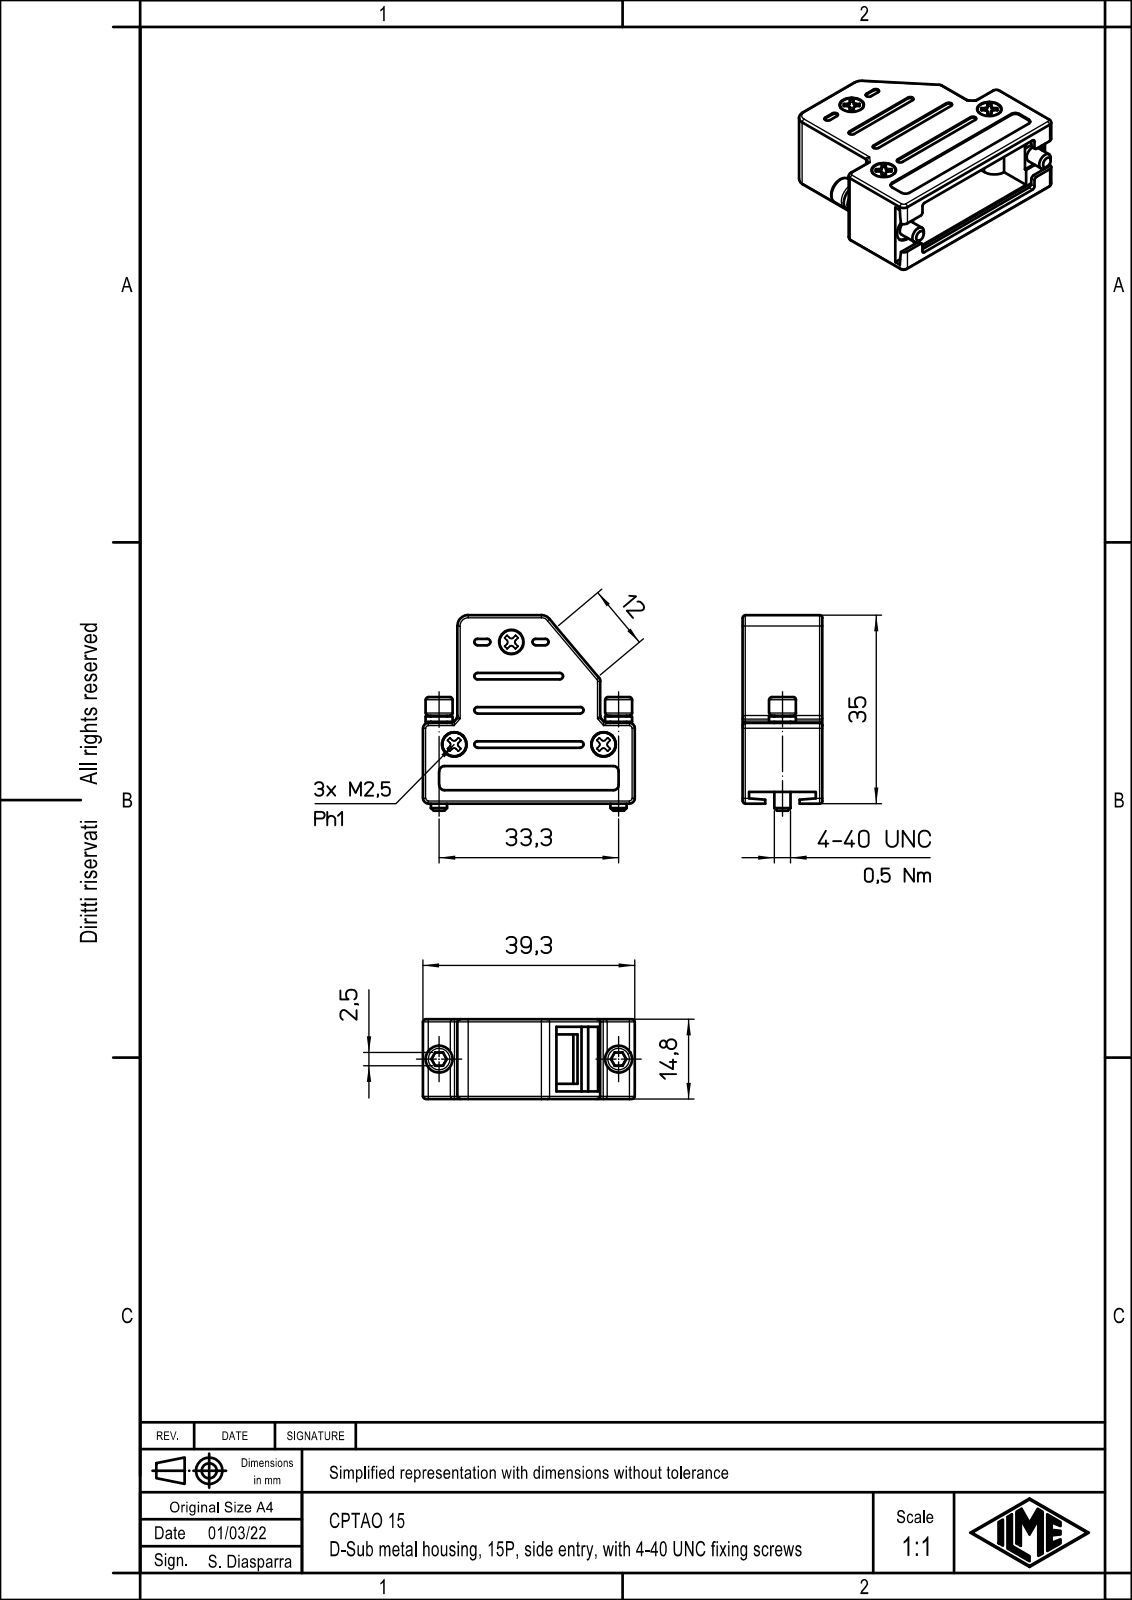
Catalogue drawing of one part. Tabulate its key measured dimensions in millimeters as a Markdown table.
| quantity | value |
| --- | --- |
| part name | CPTAO_15 |
| STEP written by | Creo Elements/Direct Modeling 20.1B 02-Apr-2019 (C) Parametric Technology GmbH (AUTOMOTIVE_DESIGN) |
| units | millimeters |
| bodies | 1 solid, 633 faces (156 planar, 203 cylindrical, 274 other) |
| overall size | 39.3 × 36.3 × 14.8 |
| volume | 6 848 mm³ |
| surface area | 6 859 mm² |
| round bosses / shafts (diameter × count) | 5 × 2, 3 × 2 |
| partial cylindrical surfaces (radius × count) | 0.5 × 40, 1 × 13, 0.6 × 10, 2 × 2, 2.1 × 2, 2.55 × 2 |
| main face-to-face distances | 1.5, 13.3, 14.8, 11.8, 1.3, 13.1, 14.6, 1.2, 6.4, 14.4 |
